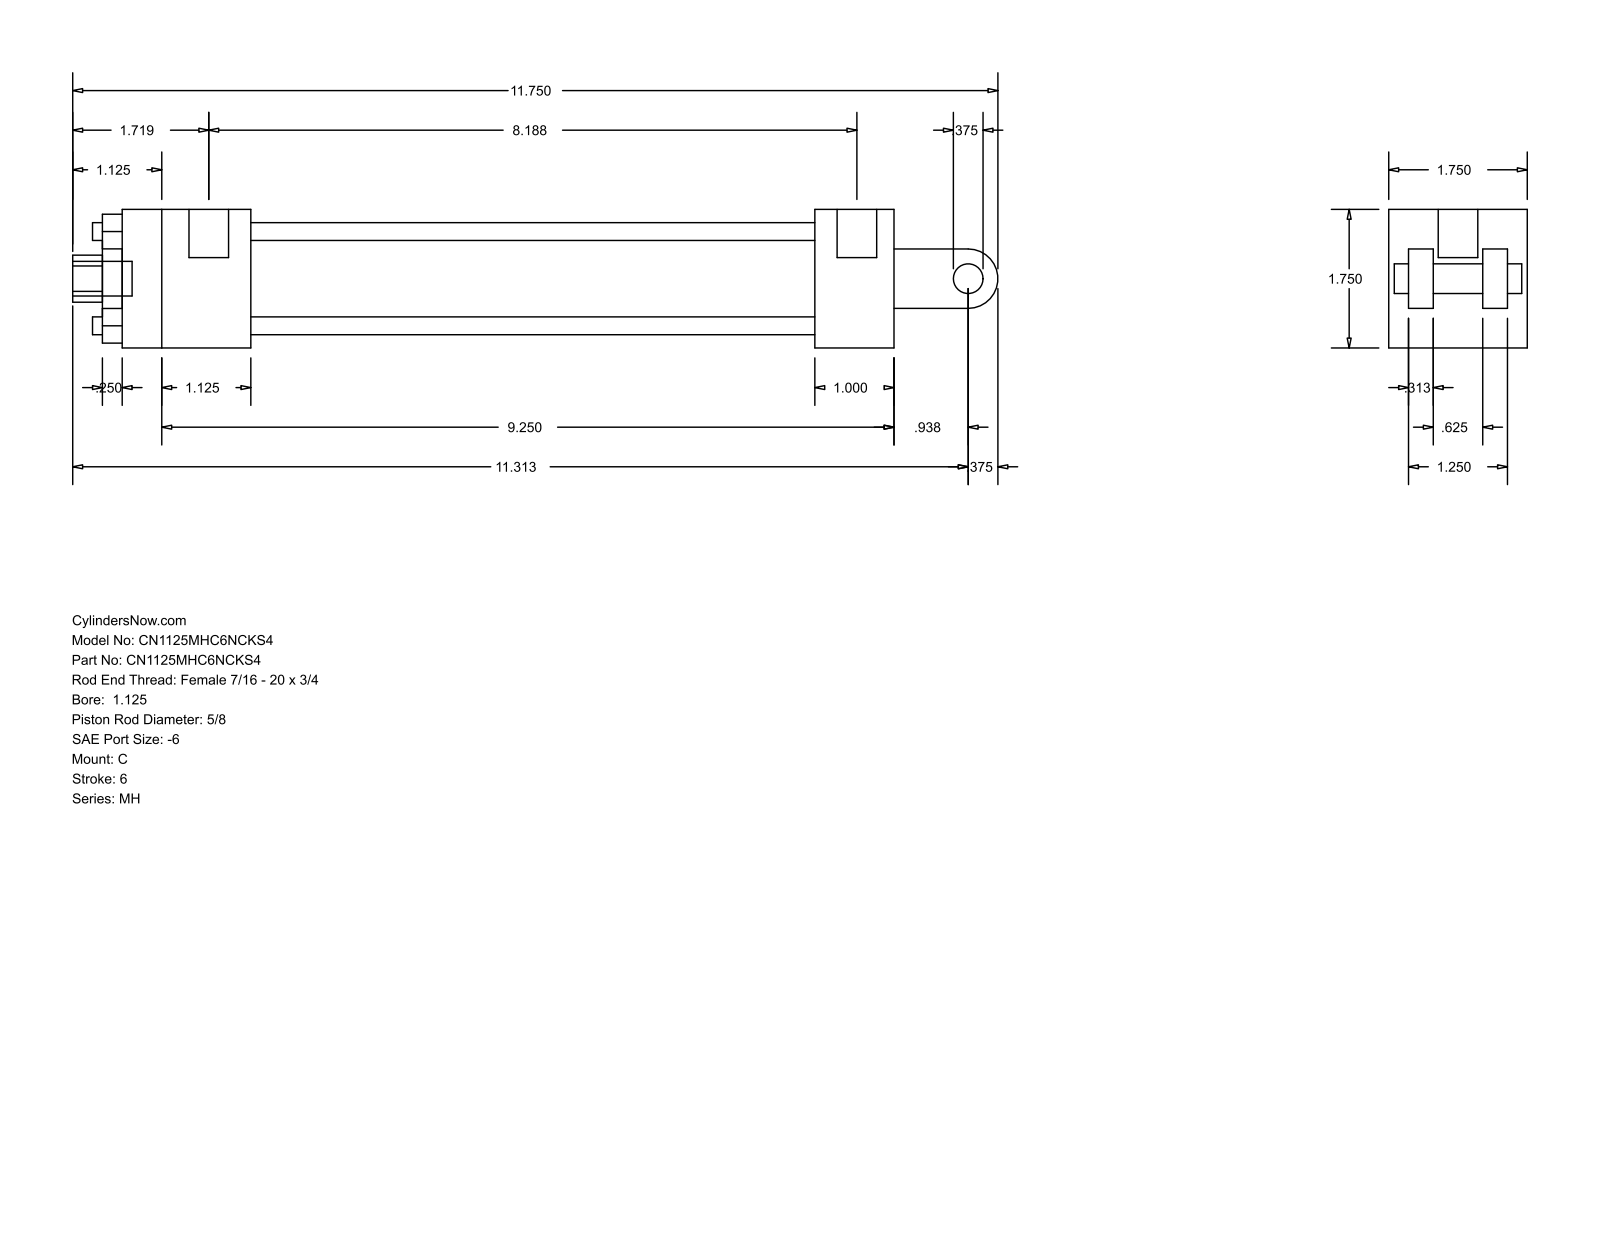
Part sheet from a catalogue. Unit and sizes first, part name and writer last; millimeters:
Units: millimetres
Overall size (bounding box): 296.86 × 44.45 × 44.45
Round holes (diameter × count): ⌀5.71 ×4, ⌀5.56 ×2, ⌀12.7 ×1, ⌀15.88 ×1, ⌀28.57 ×1, ⌀34.92 ×1
Round bosses / shafts (diameter × count): ⌀5.56 ×2, ⌀12.7 ×1, ⌀11.11 ×1, ⌀9.53 ×1
Partial cylindrical surfaces — rounded edges, fillets, slot ends (radius × count): R7.54 ×1, R9.53 ×1
Main face-to-face distances: 44.46, 6.35, 31.76, 14.29, 12.7, 30.17, 38.11, 7.94, 23.82, 25.4
Hole centre spacings: 21.37, 30.22, 42.74
Bodies: 0 solids, 99 faces (70 planar, 29 cylindrical, 0 other)
Part name (STEP PRODUCT): MH_C__0112_0.625
STEP written by: GSSL Pune (CONFIG_CONTROL_DESIGN)
